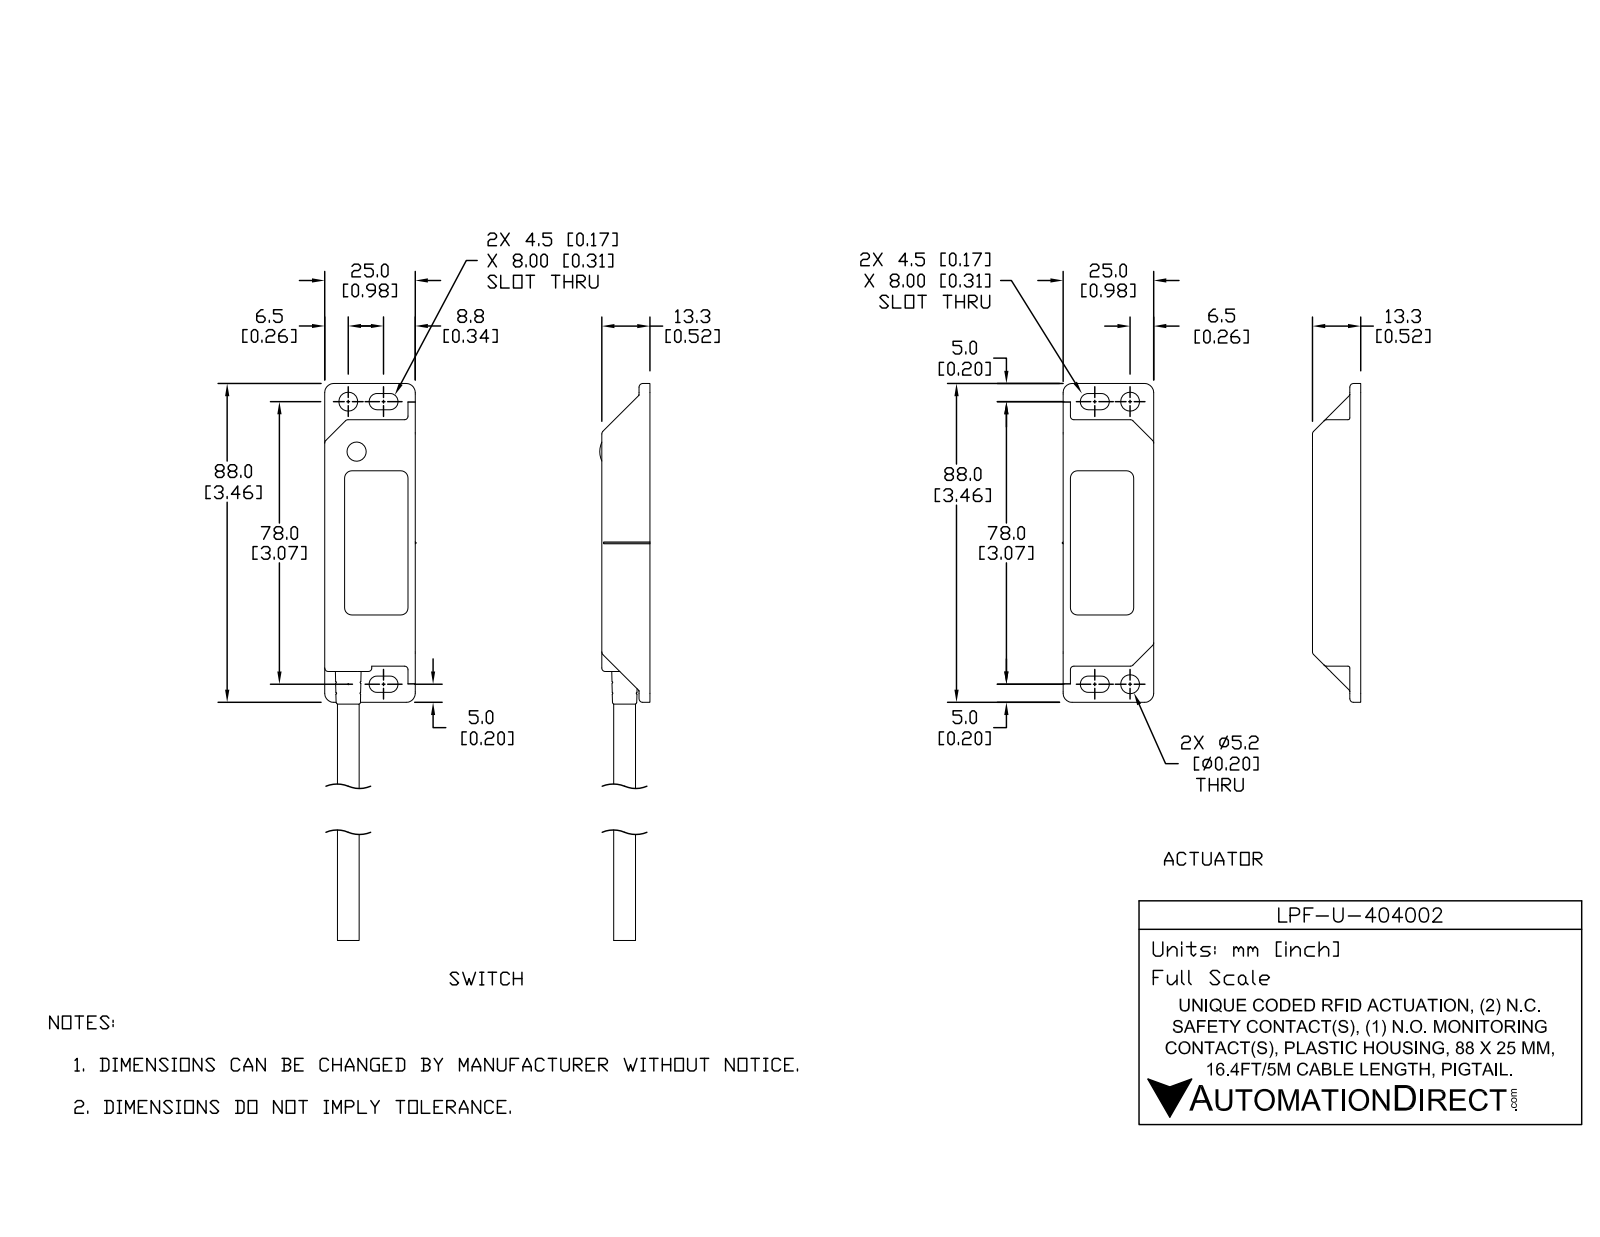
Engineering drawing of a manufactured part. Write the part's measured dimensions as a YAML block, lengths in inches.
part_name: "LPF-U-404002_2; LPF-U-404002; LPF-U-404002_1"
step_written_by: "SolidWorks 2017 (AUTOMOTIVE_DESIGN)"
units: inches
bodies: {solids: 11, faces: 1058, planar: 401, cylindrical: 303, other: 354}
overall_size: [8.849, 1.992, 0.543]
volume: 1.638
surface_area: 46.88
round_holes:
  - {diameter: 0.197, count: 4}
  - {diameter: 0.205, count: 4}
  - {diameter: 0.119, count: 1}
  - {diameter: 0.173, count: 1}
  - {diameter: 0.213, count: 1}
  - {diameter: 0.232, count: 1}
  - {diameter: 0.276, count: 1}
round_bosses_or_shafts:
  - {diameter: 0.079, count: 4}
  - {diameter: 0.193, count: 2}
  - {diameter: 0.091, count: 2}
  - {diameter: 0.339, count: 1}
  - {diameter: 0.299, count: 1}
  - {diameter: 0.28, count: 1}
  - {diameter: 0.236, count: 1}
  - {diameter: 0.209, count: 1}
partial_cylinders:
  - {radius: 0.02, count: 116}
  - {radius: 0.039, count: 49}
  - {radius: 0.079, count: 10}
  - {radius: 0.089, count: 8}
  - {radius: 0.098, count: 8}
  - {radius: 0.012, count: 6}
  - {radius: 0.189, count: 1}
face_to_face_distances: [0.067, 0.441, 0.079, 0.374, 0.059, 0.071, 0.508, 0.445, 0.512, 0.988]
hole_center_spacings: [0.748, 1.097, 1.19, 1.275, 1.48, 1.571, 1.784, 1.895]
